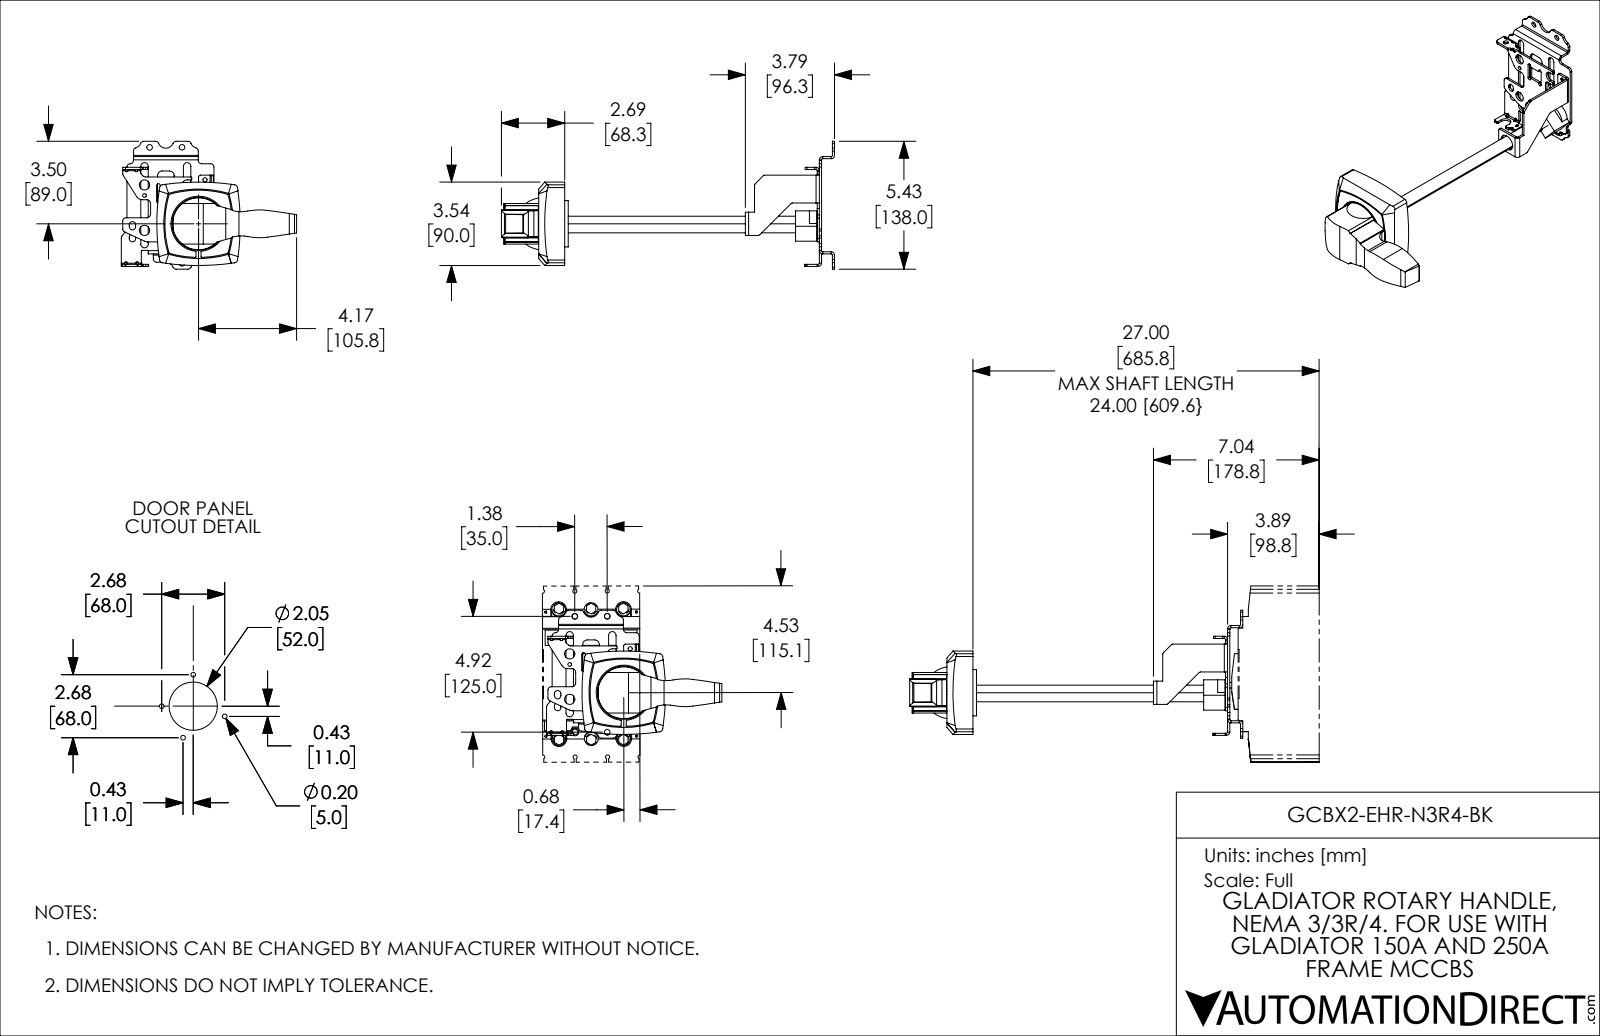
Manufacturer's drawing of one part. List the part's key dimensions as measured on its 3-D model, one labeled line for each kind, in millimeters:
Part name (STEP PRODUCT): GCBX2-EHR-N3R4-BK
STEP written by: SolidWorks 2021 (CONFIG_CONTROL_DESIGN)
Units: millimetres
Bodies: 8 solids, 506 faces (241 planar, 106 cylindrical, 159 other)
Overall size (bounding box): 359.56 × 189.14 × 138
Volume: 428 243 mm³ · Surface area: 107 172 mm²
Round holes (diameter × count): ⌀5 ×4, ⌀6 ×3, ⌀50 ×1, ⌀57 ×1
Round bosses / shafts (diameter × count): ⌀59.5 ×1, ⌀50 ×1, ⌀11 ×1
Partial cylindrical surfaces — rounded edges, fillets, slot ends (radius × count): R0.5 ×12, R1.27 ×8, R3.57 ×8, R3 ×4, R3.5 ×4, R113.75 ×4, R257.5 ×4, R262 ×4
Main face-to-face distances: 2.3, 12.7, 278.88, 276.58, 4.6, 274.28, 16.3, 14, 301.78, 299.48
Hole centre spacings: 34, 35.74, 68.88, 10.93, 35, 41.05, 45.51, 46.12
